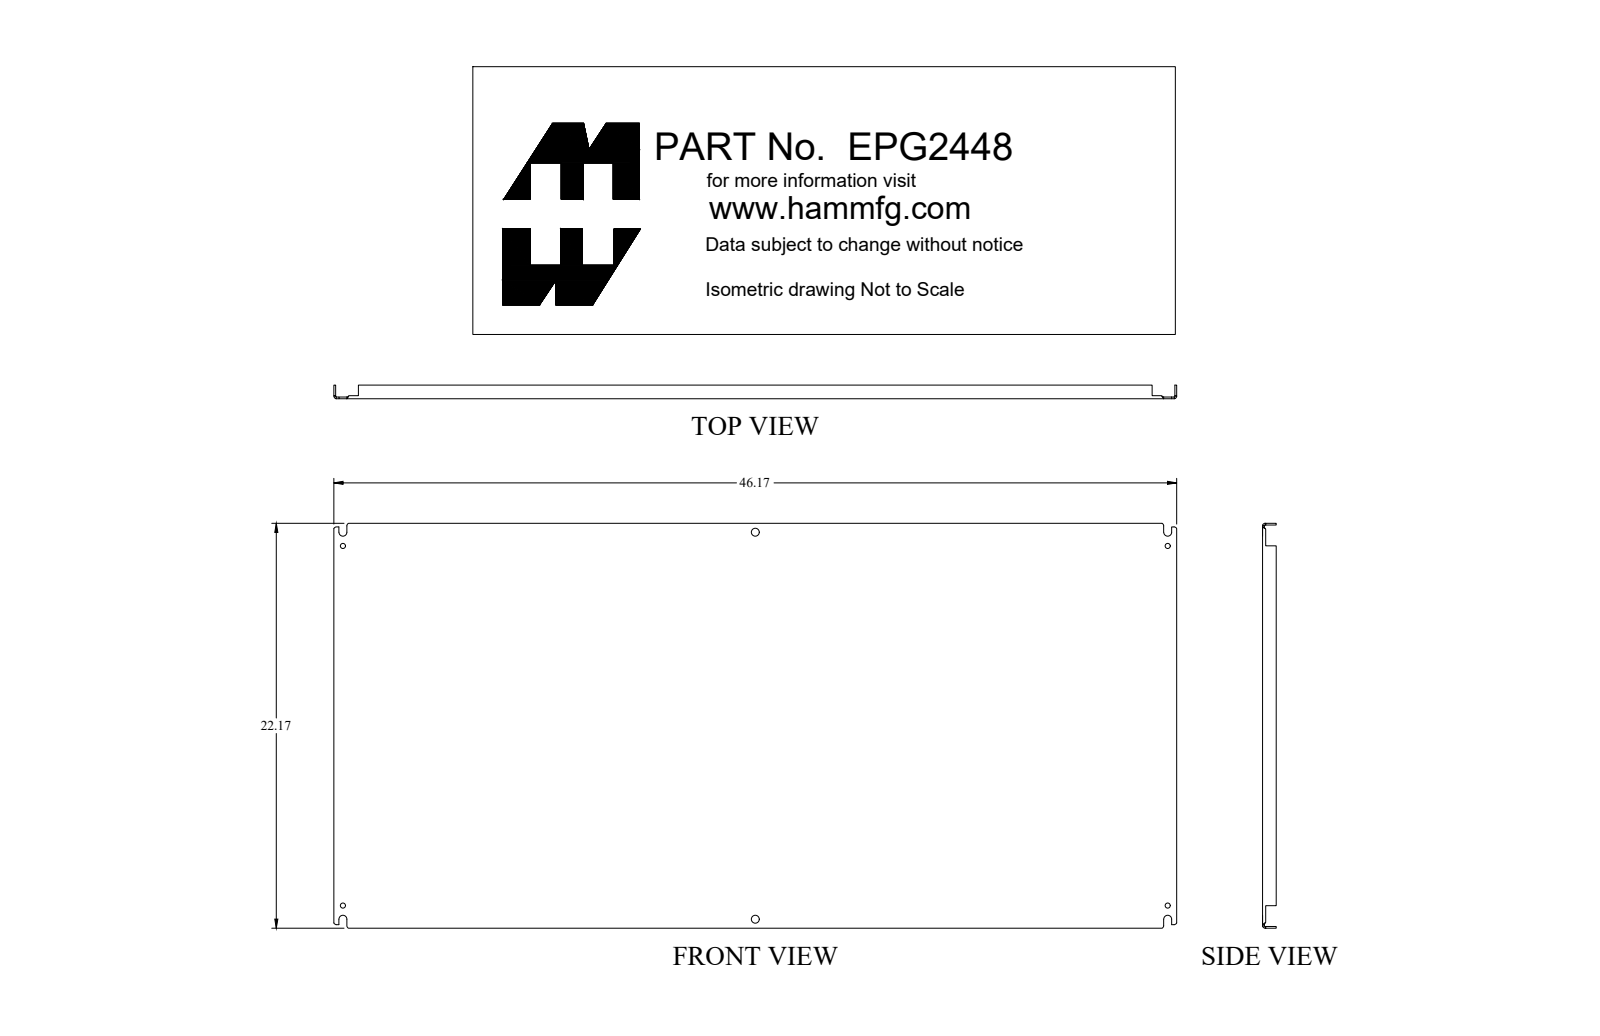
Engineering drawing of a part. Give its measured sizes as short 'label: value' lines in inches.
name: EPG2448
written by: SolidWorks 2018 (AUTOMOTIVE_DESIGN)
unit: in
bodies: 1 solid, 132 faces (74 planar, 42 cylindrical, 16 other)
size: 40.17 × 28.17 × 0.75
volume: 114.7 in³; area: 2 429 in²
holes: 4× ⌀0.281, 2× ⌀0.437
rounds: 4× R0.048, 4× R0.063, 4× R0.143, 4× R0.219
face distances: 0.095, 28.075, 40.075, 28.17, 27.98, 39.98, 40.17, 0.75, 0.655, 0.171
hole spacings: 19.608, 32.907, 25.688, 39.188, 46.857, 27.188
